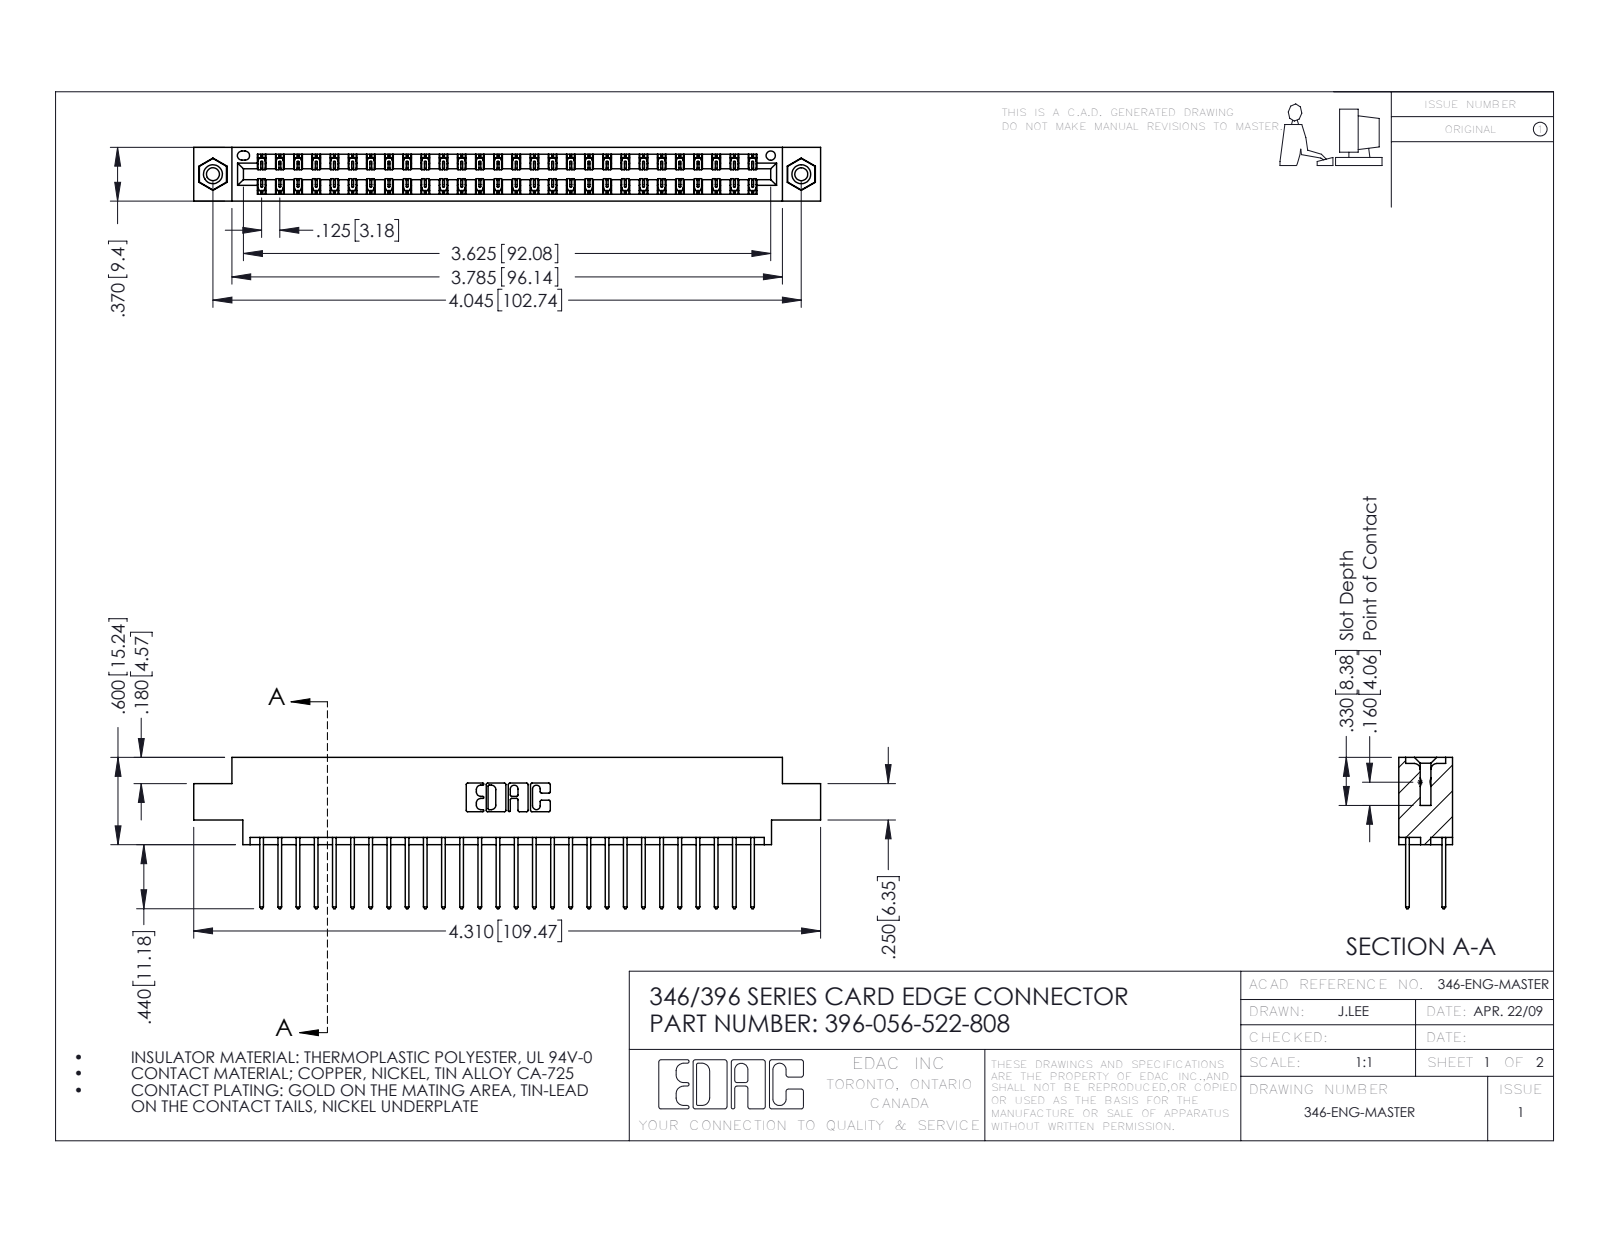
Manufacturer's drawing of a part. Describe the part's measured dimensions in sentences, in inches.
The part is named "396-056-522-808; 345-250-001_345-250-003-102; 346 Part_0.170 Offset - 0.156 Dia-TI; 345-292-001_345-293-122". Its 3-D file was written by "SolidWorks 2016 (CONFIG_CONTROL_DESIGN)". It is 59 solids with 3098 faces: 2072 planar, 1010 cylindrical and 16 other. Overall it measures 4.31 by 1.04 by 0.37 inches. Its volume is 0.644 cubic inches and its surface area 23.47 square inches. Round holes: 2 of diameter 0.089, 2 of diameter 0.125, 2 of diameter 0.156, 1 of diameter 0.064. Round bosses or shafts: 2 of diameter 0.155. Partial cylindrical surfaces (rounded edges, fillets, slot ends): 84 of radius 0.006, 56 of radius 0.01, 22 of radius 0.01, 6 of radius 0.007, 6 of radius 0.031, 3 of radius 0.026, 2 of radius 0.014, 2 of radius 0.022. The main face-to-face distances are 0.048, 0.322, 0.25, 0.37, 0.072, 0.298, 0.025, 0.275, 0.222, 0.148. The hole center spacings are 0.246, 3.837, 4.045.
